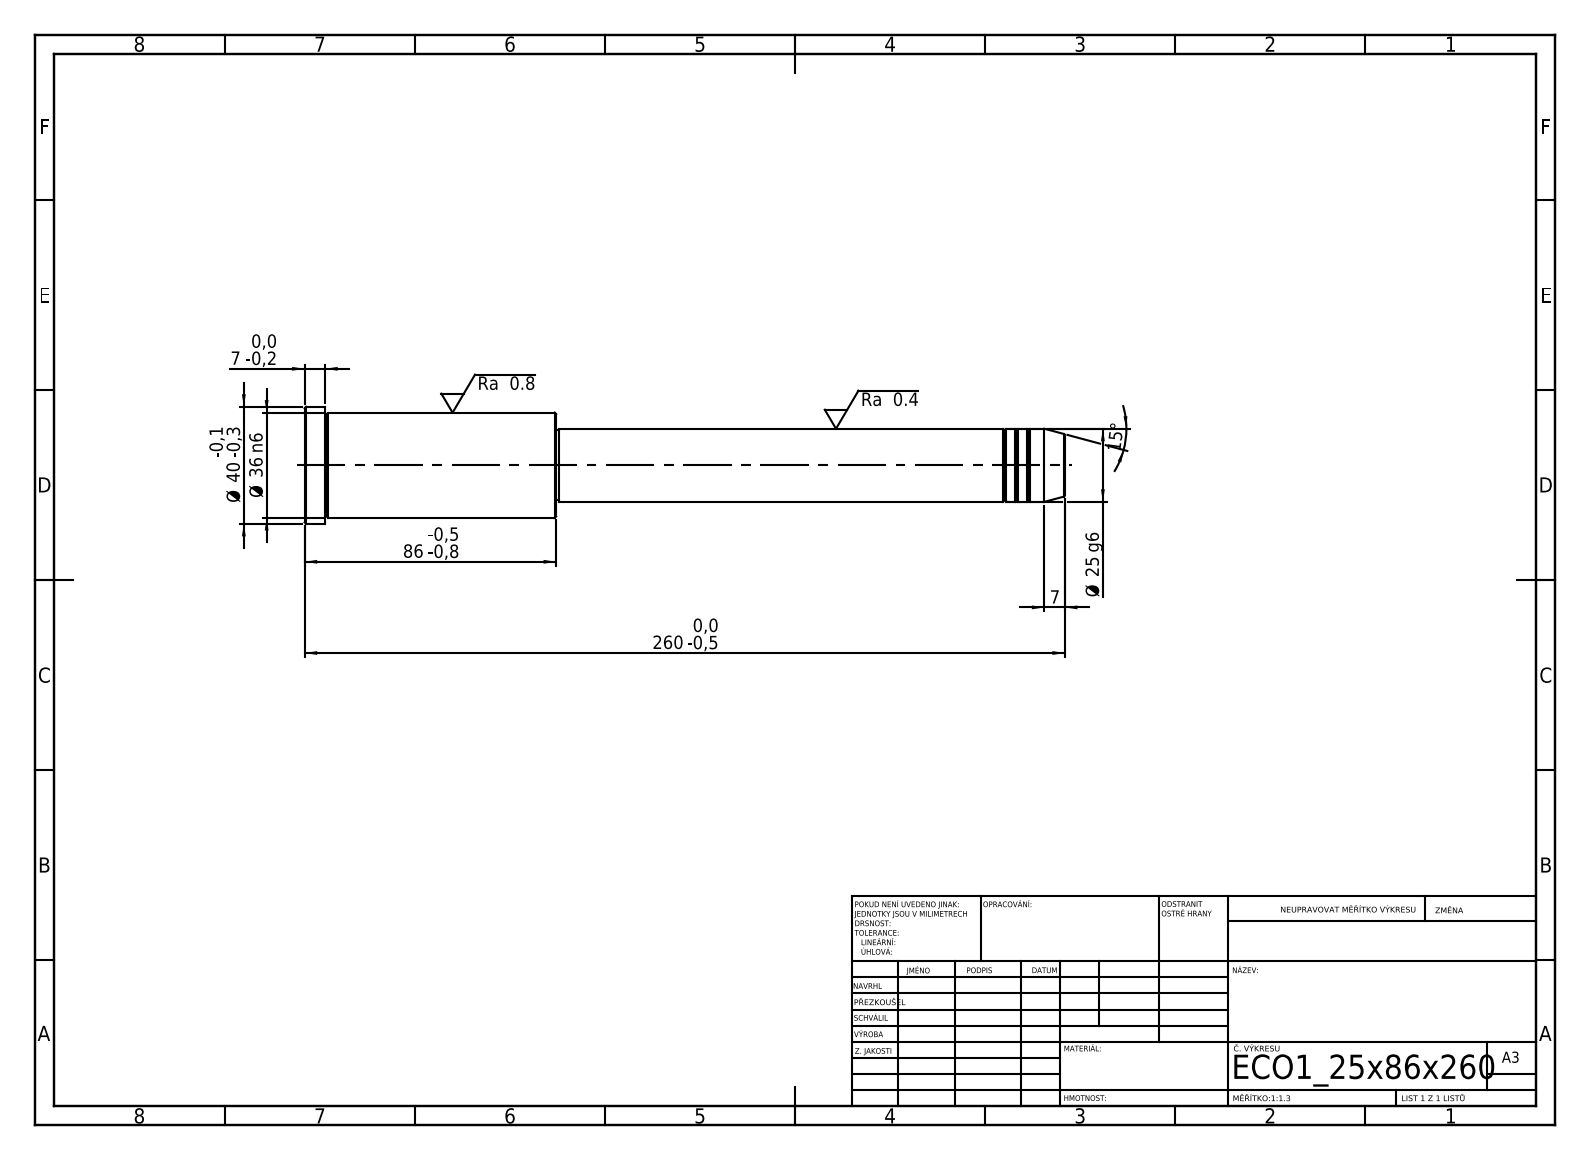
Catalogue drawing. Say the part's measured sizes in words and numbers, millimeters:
Its 3-D file was written by "SolidWorks 2019 (CONFIG_CONTROL_DESIGN)". It is 1 solid with 43 faces: 5 planar, 14 cylindrical and 24 other. Overall it measures 260 by 40 by 40 millimeters. Its volume is 173 926 cubic millimeters and its surface area 26 016 square millimeters. Round bosses or shafts: 1 of diameter 40, 1 of diameter 36, 1 of diameter 25, 1 of diameter 24. The main face-to-face distances are 86, 174, 260, 253, 79, 7, 173, 1, 80, 87.
